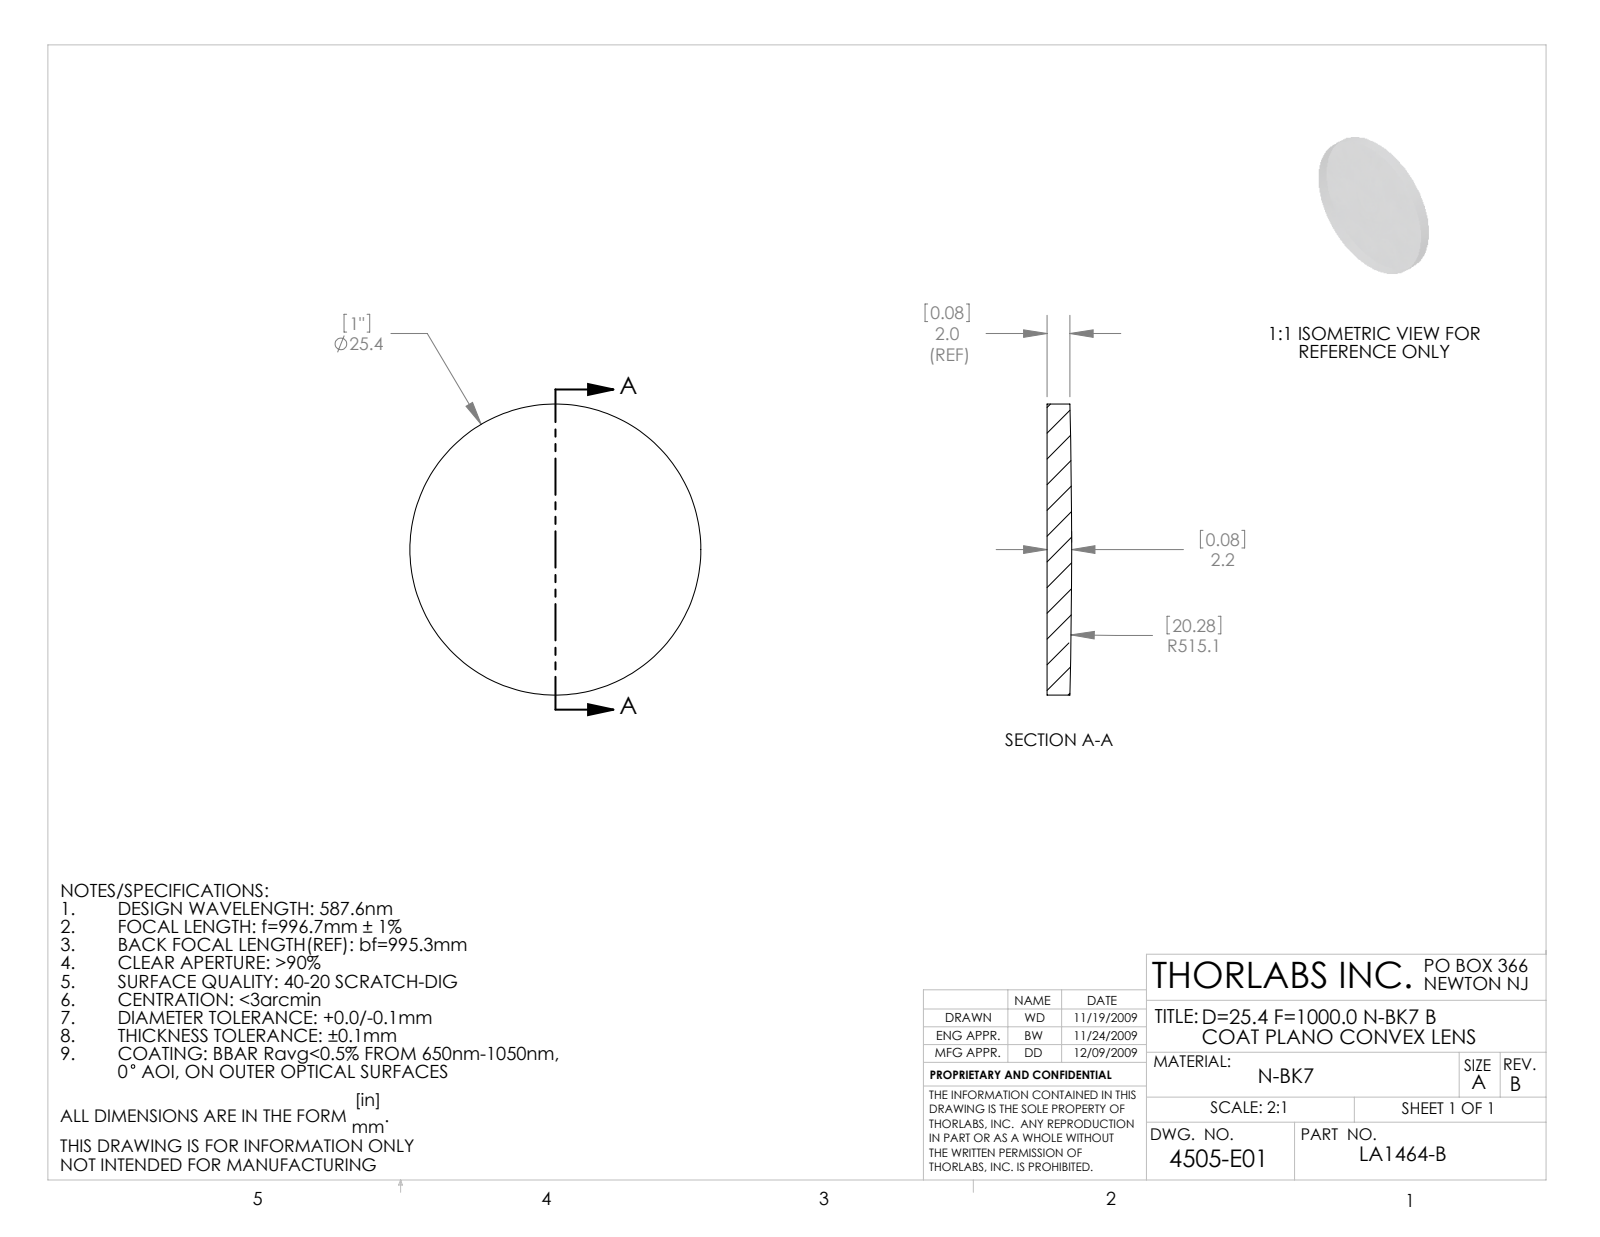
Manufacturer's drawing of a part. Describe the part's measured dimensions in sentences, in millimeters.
The part is named "4505-E0W". Its 3-D file was written by "SolidWorks 2009 (AUTOMOTIVE_DESIGN)". It is 1 solid with 5 faces: 1 planar, 2 cylindrical and 2 other. Overall it measures 25.4 by 25.4 by 2.15 millimeters. Its volume is 1 050 cubic millimeters and its surface area 1 173 square millimeters. Round bosses or shafts: 1 of diameter 25.4.
